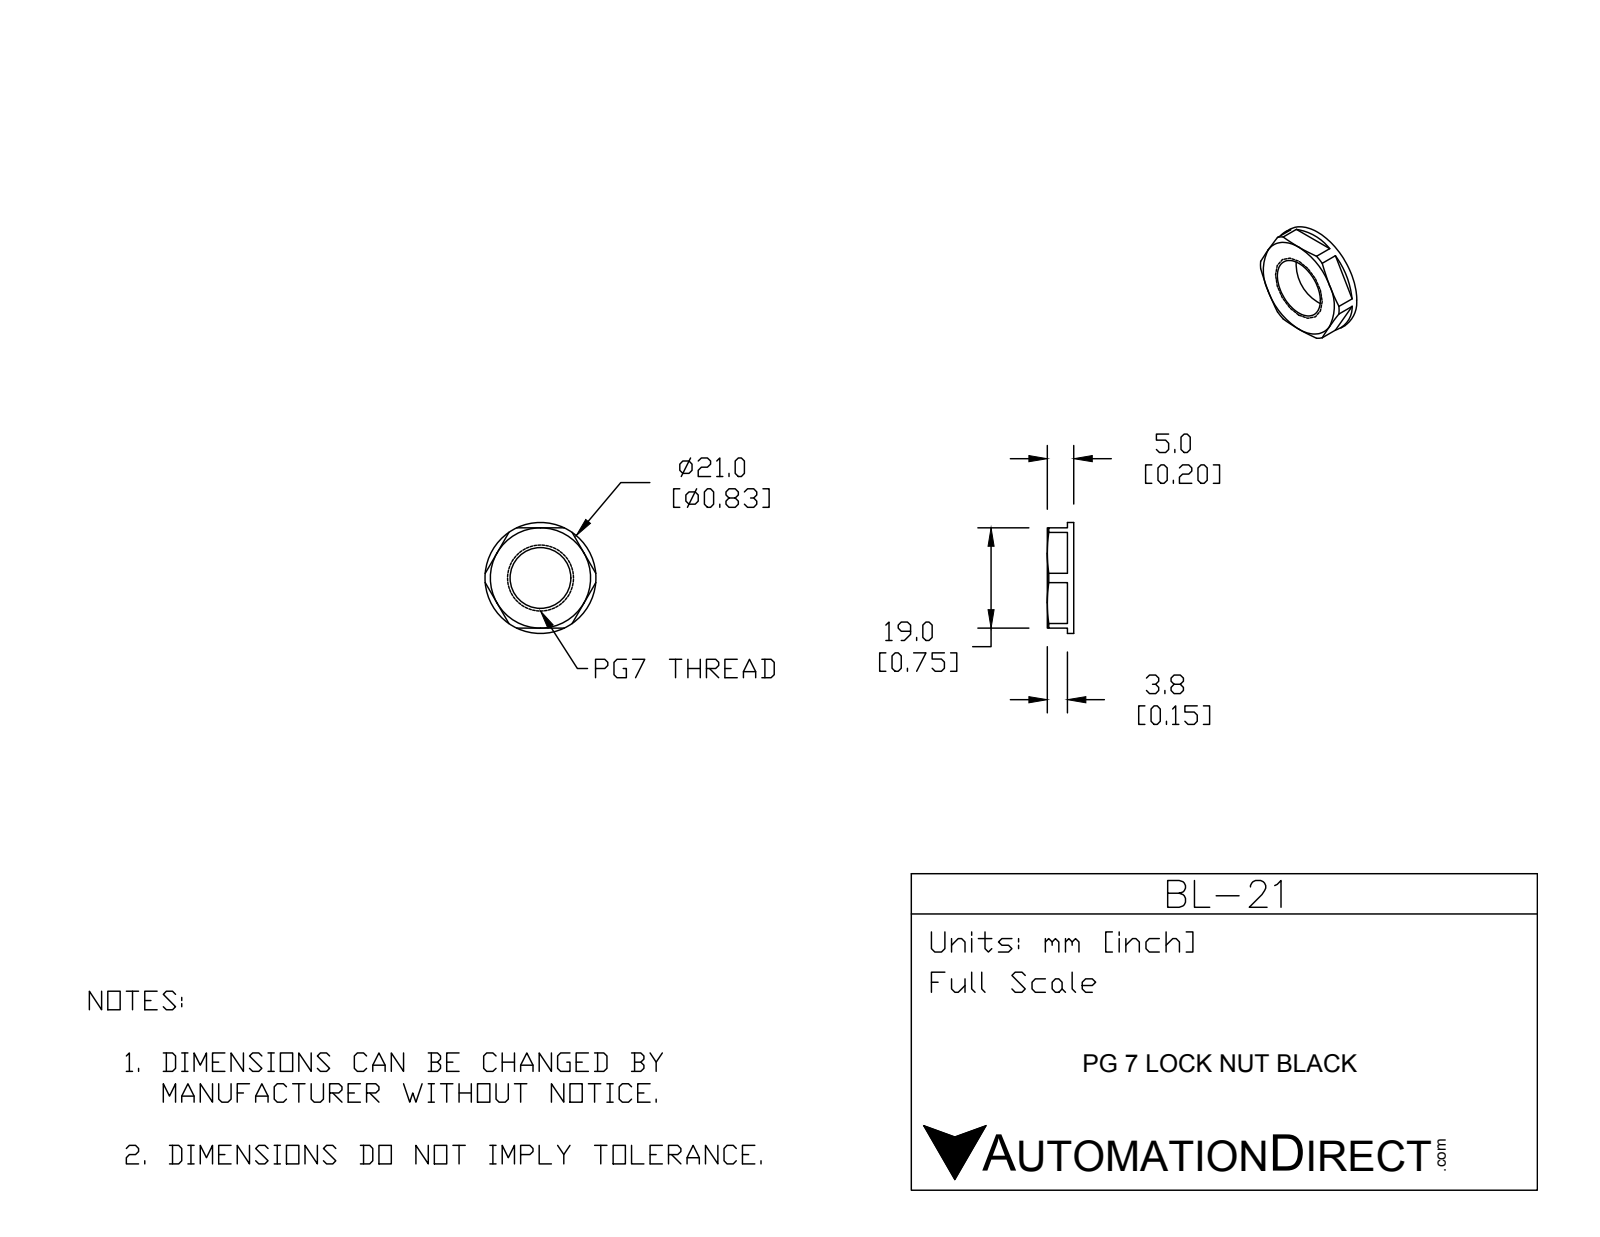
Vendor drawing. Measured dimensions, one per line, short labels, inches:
name: BL-21
written by: SolidWorks 2015 (CONFIG_CONTROL_DESIGN)
unit: in
bodies: 1 solid, 33 faces (17 planar, 10 cylindrical, 6 other)
size: 0.827 × 0.827 × 0.197
volume: 0.065 in³; area: 1.53 in²
holes: 3× ⌀0.059, 1× ⌀0.453
bosses: 1× ⌀0.827
face distances: 0.197, 0.748, 0.047, 0.15, 0.035, 0.185
hole spacings: 0.356, 0.617, 0.617
